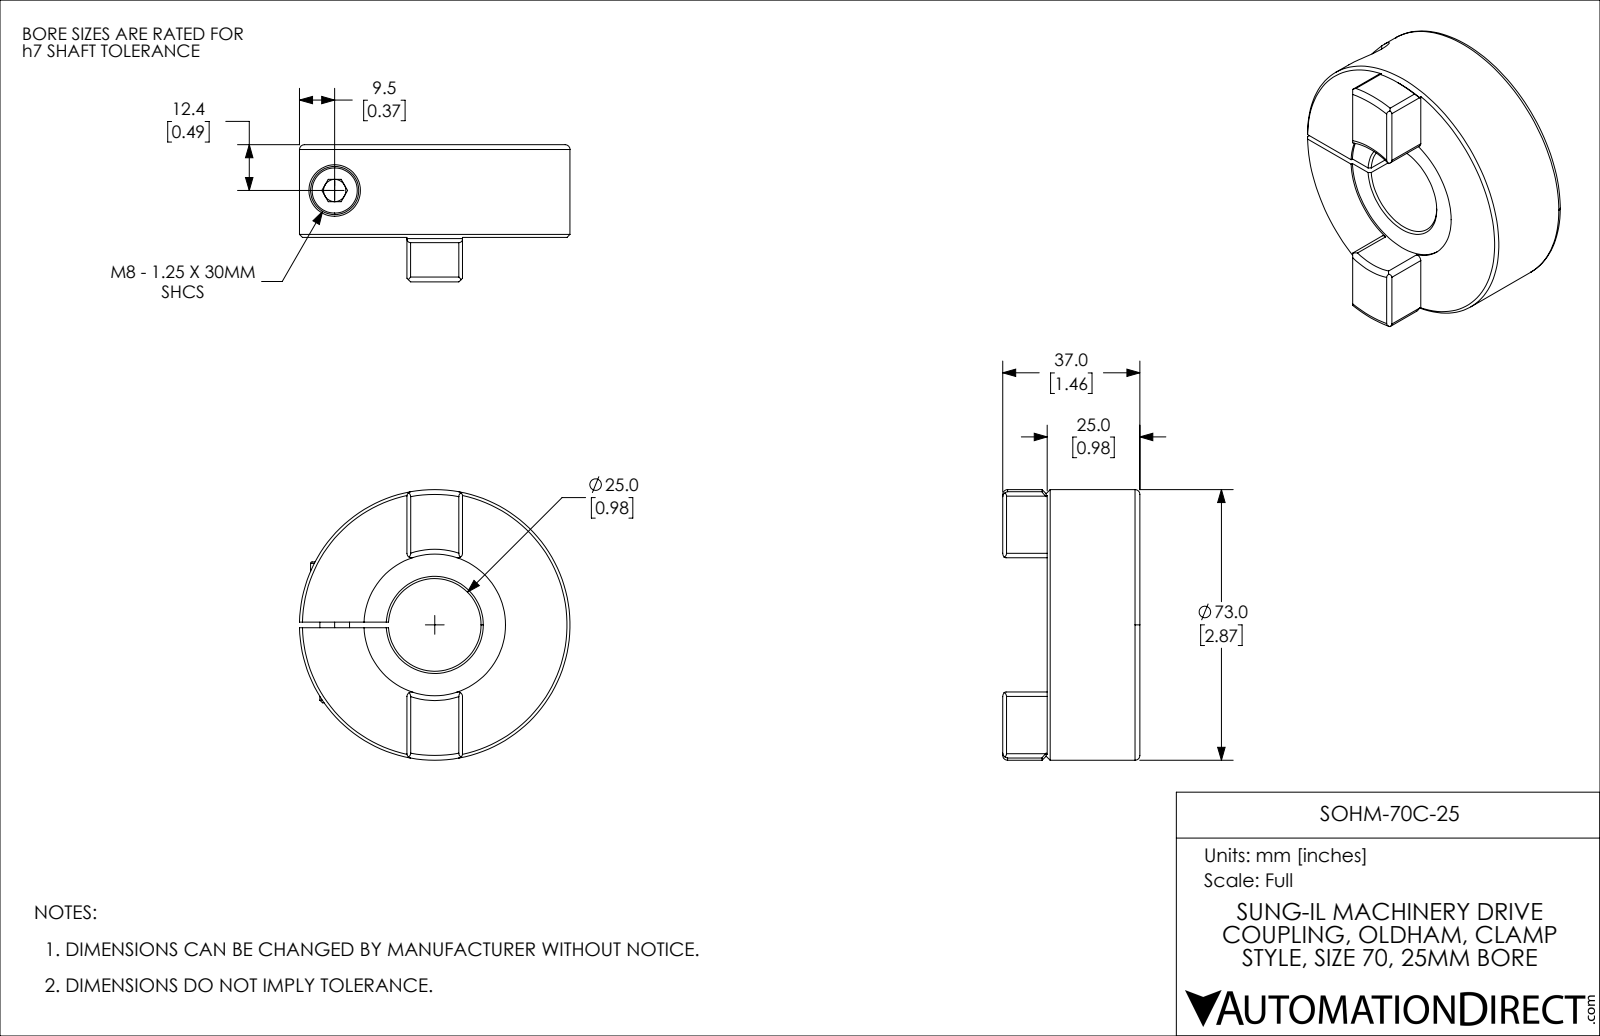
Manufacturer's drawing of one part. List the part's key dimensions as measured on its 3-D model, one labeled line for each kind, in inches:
Part name (STEP PRODUCT): SOHM-70C-25
STEP written by: SolidWorks 2021 (CONFIG_CONTROL_DESIGN)
Units: inches
Bodies: 2 solids, 90 faces (35 planar, 30 cylindrical, 25 other)
Overall size (bounding box): 2.874 × 2.874 × 1.457
Volume: 5.848 in³ · Surface area: 30.98 in²
Round holes (diameter × count): ⌀0.236 ×1, ⌀0.268 ×1, ⌀0.335 ×1, ⌀0.547 ×1, ⌀0.984 ×1, ⌀1.504 ×1
Round bosses / shafts (diameter × count): ⌀2.874 ×1, ⌀0.512 ×1, ⌀0.315 ×1
Partial cylindrical surfaces — rounded edges, fillets, slot ends (radius × count): R0.047 ×8, R1.969 ×1
Main face-to-face distances: 0.984, 0.059, 0.965, 0.02, 1.457, 0.492, 0.472, 0.591, 0.384, 0.325
